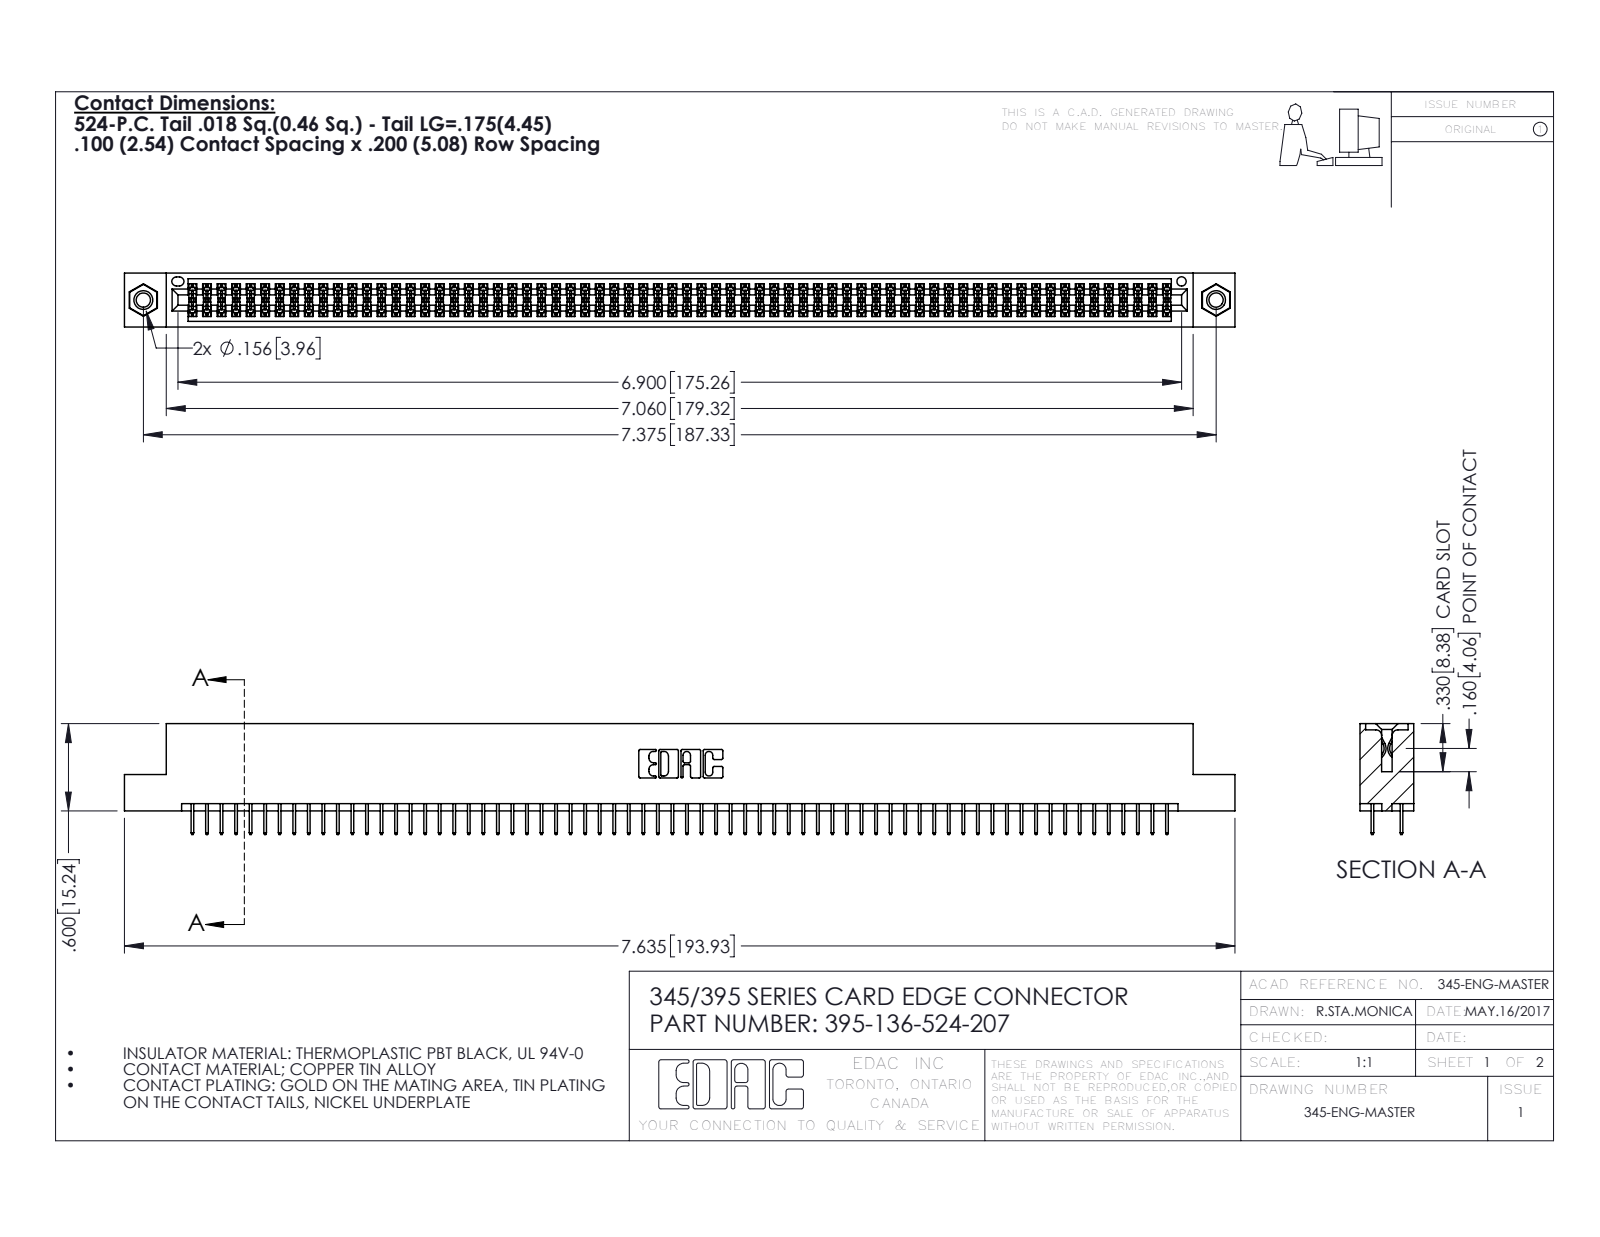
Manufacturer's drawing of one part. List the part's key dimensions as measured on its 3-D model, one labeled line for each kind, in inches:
Part name (STEP PRODUCT): 395-136-524-207; 345-292-001_345-293-124; 345 Part_Flush Mounting Lugs - 0.156 Dia-TI; 345-250-001_345-250-005-103
STEP written by: SolidWorks 2016 (CONFIG_CONTROL_DESIGN)
Units: inches
Bodies: 139 solids, 7530 faces (5416 planar, 2098 cylindrical, 16 other)
Overall size (bounding box): 7.635 × 0.762 × 0.37
Volume: 1.151 in³ · Surface area: 43.19 in²
Round holes (diameter × count): ⌀0.098 ×2, ⌀0.125 ×2, ⌀0.156 ×2, ⌀0.064 ×1
Round bosses / shafts (diameter × count): ⌀0.155 ×2
Partial cylindrical surfaces — rounded edges, fillets, slot ends (radius × count): R0.006 ×204, R0.01 ×22, R0.007 ×6, R0.031 ×6, R0.026 ×3, R0.014 ×2, R0.019 ×2, R0.022 ×2
Main face-to-face distances: 0.072, 0.298, 0.2, 0.37, 0.098, 0.272, 0.025, 0.225, 0.072, 0.175
Hole centre spacings: 0.27, 7.139, 7.375
